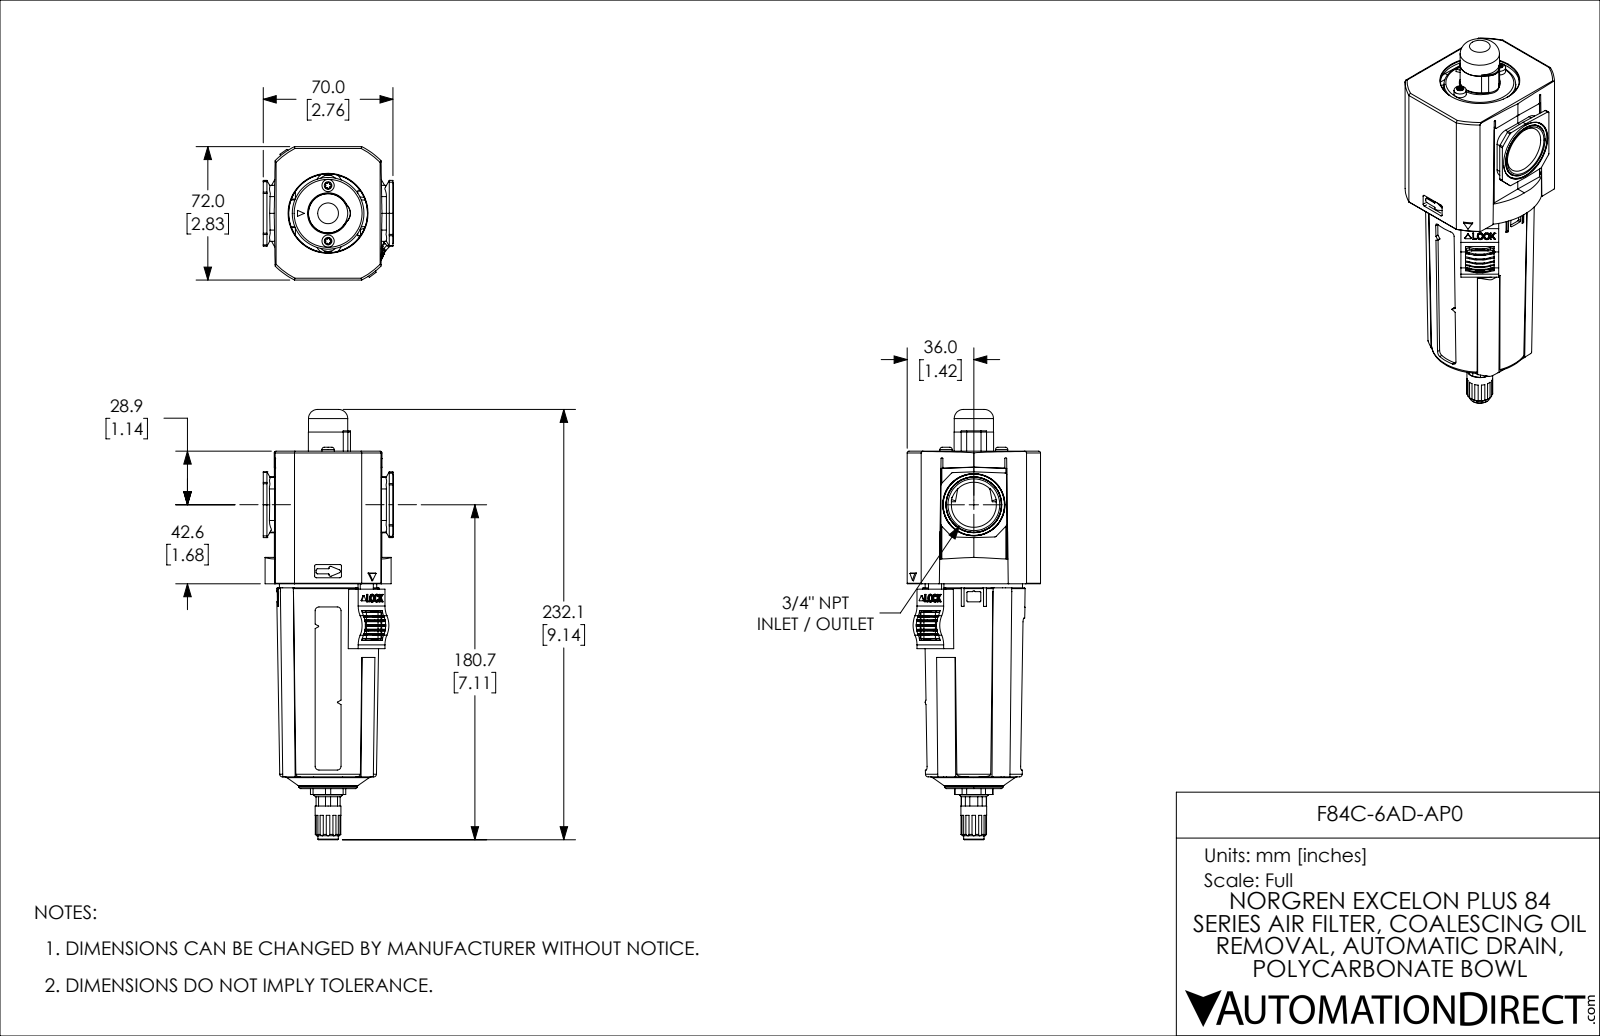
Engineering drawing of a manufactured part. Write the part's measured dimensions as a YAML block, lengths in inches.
part_name: "F84C-6AD-AP0"
step_written_by: "SolidWorks 2021 (CONFIG_CONTROL_DESIGN)"
units: inches
bodies: {solids: 7, faces: 1207, planar: 546, cylindrical: 467, other: 194}
overall_size: [9.139, 2.835, 2.766]
volume: 28.55
surface_area: 157.1
round_holes:
  - {diameter: 0.163, count: 2}
  - {diameter: 0.177, count: 2}
  - {diameter: 0.22, count: 1}
  - {diameter: 0.246, count: 1}
  - {diameter: 0.776, count: 1}
  - {diameter: 0.969, count: 1}
  - {diameter: 2.461, count: 1}
round_bosses_or_shafts:
  - {diameter: 0.315, count: 2}
  - {diameter: 0.276, count: 2}
  - {diameter: 0.26, count: 2}
  - {diameter: 1.524, count: 1}
  - {diameter: 1, count: 1}
  - {diameter: 0.969, count: 1}
  - {diameter: 0.907, count: 1}
  - {diameter: 0.835, count: 1}
partial_cylinders:
  - {radius: 0.02, count: 60}
  - {radius: 0.039, count: 44}
  - {radius: 0.01, count: 24}
  - {radius: 0.028, count: 16}
  - {radius: 0.008, count: 10}
  - {radius: 0.038, count: 8}
  - {radius: 0.045, count: 8}
  - {radius: 0.06, count: 8}
face_to_face_distances: [2.835, 2.411, 0.059, 0.035, 2.376, 1.951, 1.915, 0.461, 2.352, 2.317]
hole_center_spacings: [0.591, 0.594, 1.185, 1.181, 1.189]
